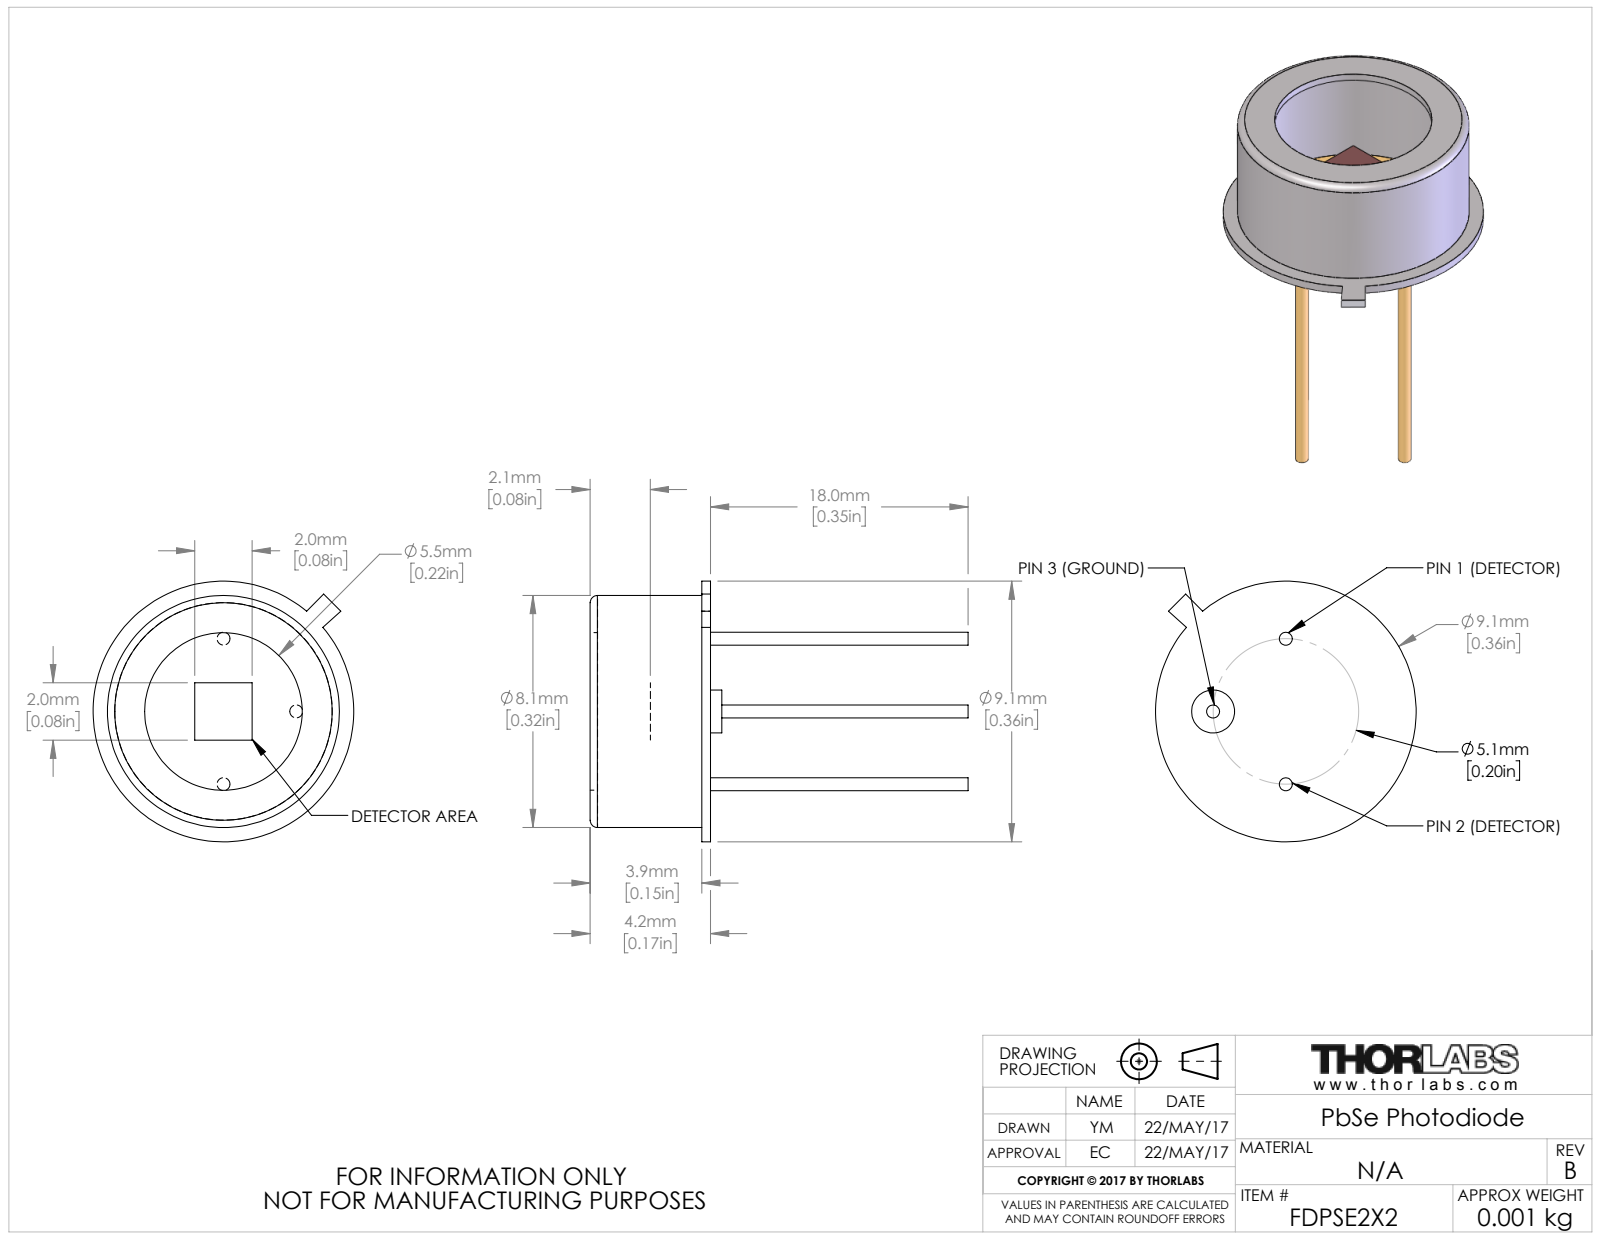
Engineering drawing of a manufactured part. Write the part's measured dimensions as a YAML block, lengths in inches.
part_name: "24701-E0W"
step_written_by: "SolidWorks 2016 (AUTOMOTIVE_DESIGN)"
units: inches
bodies: {solids: 2, faces: 37, planar: 18, cylindrical: 17, other: 2}
overall_size: [0.52, 0.358, 0.358]
volume: 0.003
surface_area: 0.665
round_holes:
  - {diameter: 0.217, count: 1}
  - {diameter: 0.299, count: 1}
round_bosses_or_shafts:
  - {diameter: 0.018, count: 3}
  - {diameter: 0.358, count: 1}
  - {diameter: 0.319, count: 1}
  - {diameter: 0.059, count: 1}
face_to_face_distances: [0.154, 0.156, 0.165, 0.163, 0.144, 0.083, 0.081, 0.071, 0.073, 0.063]
